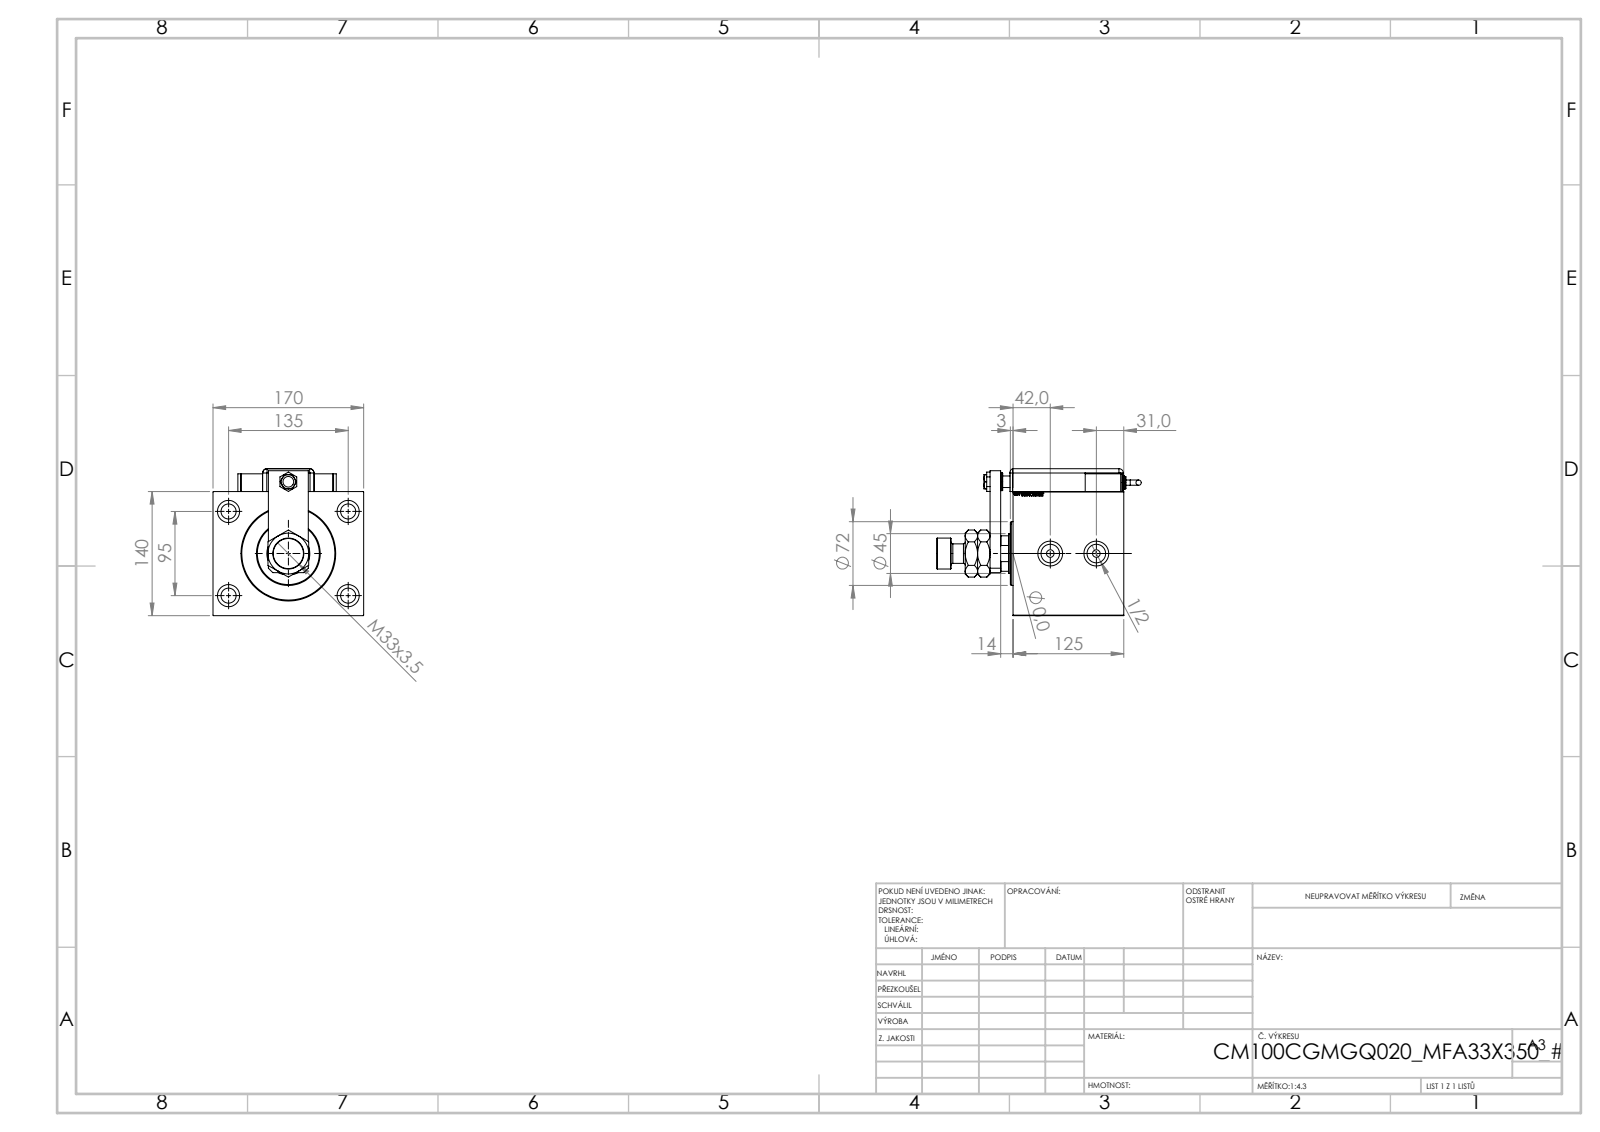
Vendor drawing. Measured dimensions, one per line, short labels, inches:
name: SWITCH_Q_FRONT_BACK; V450CM_VC_B; ZARAZKA_Q; TYC (+8 more)
written by: SolidWorks 2019 (CONFIG_CONTROL_DESIGN)
unit: in
bodies: 14 solids, 1302 faces (632 planar, 121 cylindrical, 549 other)
size: 9.085 × 6.693 × 6.528
volume: 183.4 in³; area: 482 in²
holes: 4× ⌀0.669, 4× ⌀0.984, 2× ⌀0.157, 2× ⌀0.315, 2× ⌀0.335, 2× ⌀0.825, 2× ⌀1.102, 1× ⌀0.472, 1× ⌀0.512, 1× ⌀0.551, 1× ⌀1.24, 1× ⌀1.299
bosses: 3× ⌀0.787, 2× ⌀0.63, 2× ⌀0.551, 2× ⌀0.236, 1× ⌀2.835, 1× ⌀1.378, 1× ⌀0.866
rounds: 9× R0.197, 1× R0.394, 1× R0.866
face distances: 5.512, 4.921, 2.008, 6.693, 2.913, 0.118, 0.394, 3.031, 0.85, 1.157
hole spacings: 3.25, 2.967, 3.74, 5.315, 5.715, 6.499, 0.787, 2.047
